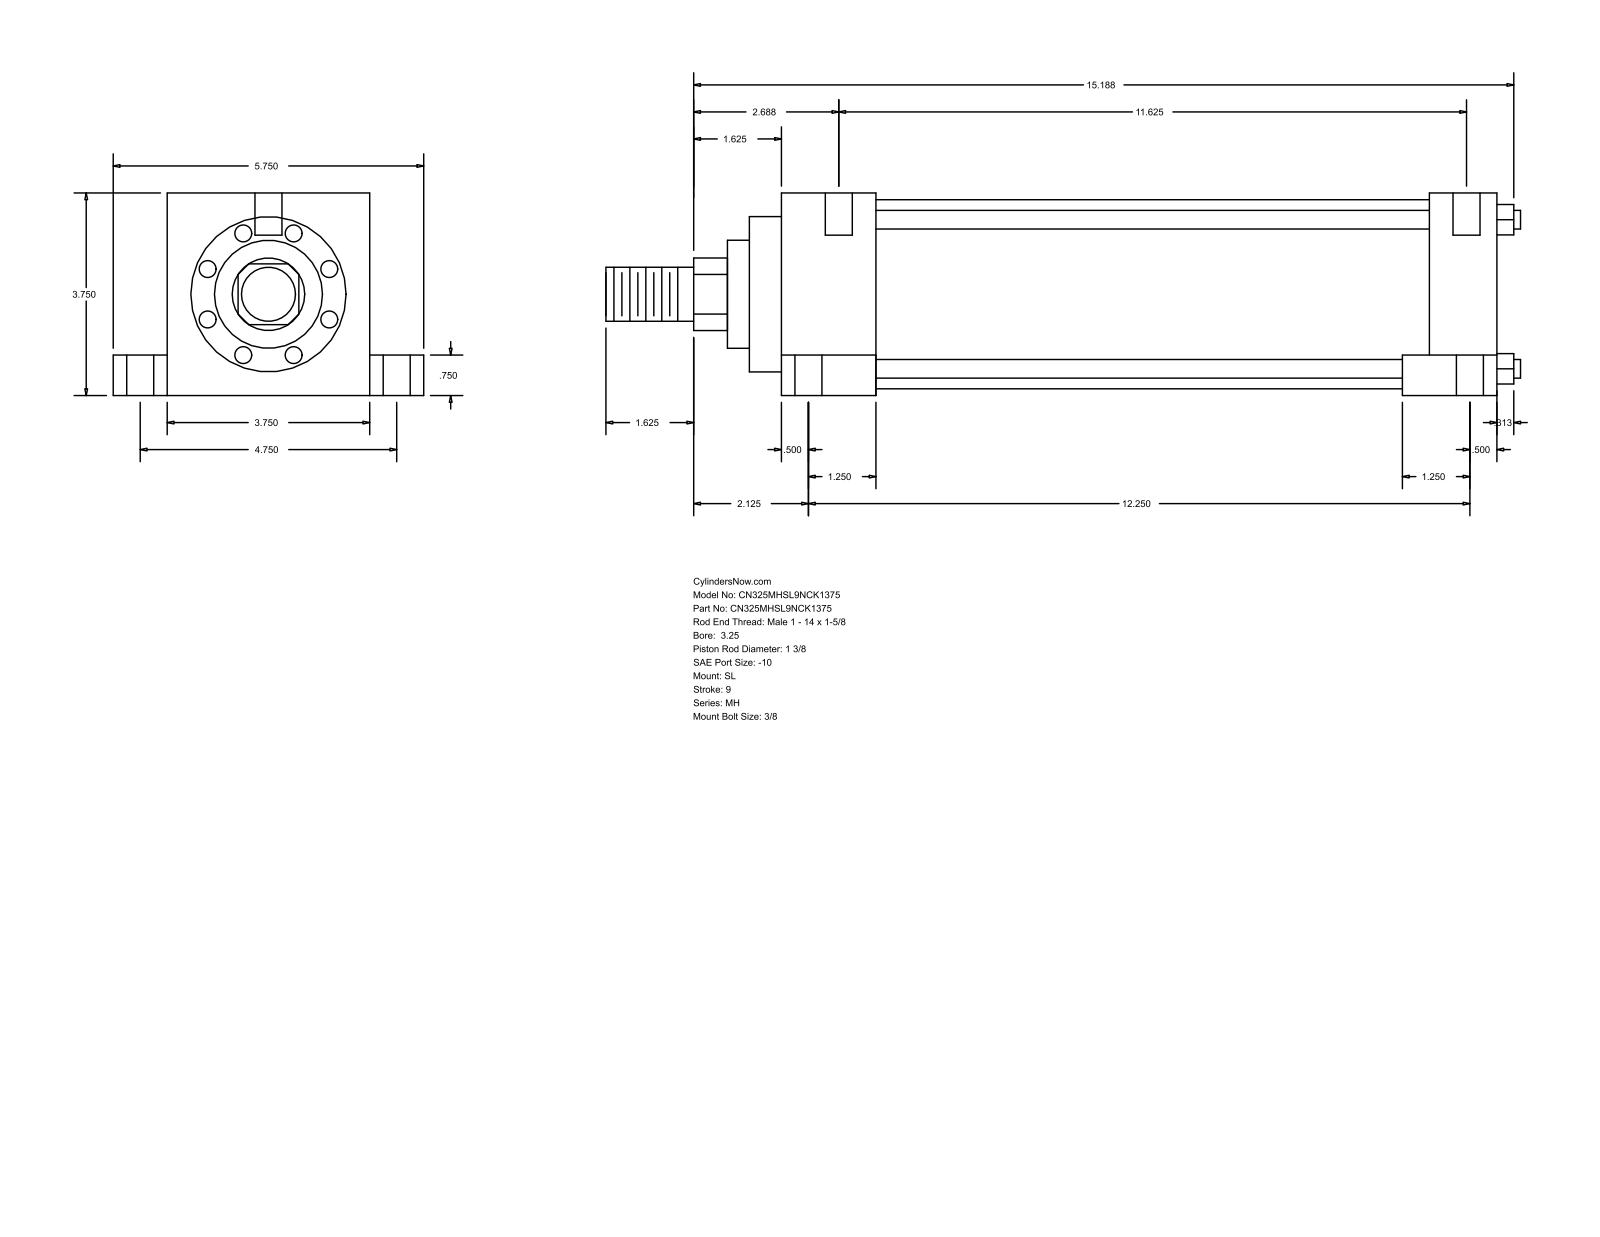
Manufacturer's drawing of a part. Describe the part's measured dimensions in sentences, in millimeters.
The part is named "MH_SL__0325_1.375". Its 3-D file was written by "GSSL Pune (CONFIG_CONTROL_DESIGN)". It is 0 solids with 110 faces: 77 planar, 33 cylindrical and 0 other. Overall it measures 430.21 by 146.05 by 95.25 millimeters. Round holes: 6 of diameter 12.7, 4 of diameter 5.56, 4 of diameter 19.05. Round bosses or shafts: 4 of diameter 8.76, 1 of diameter 88.9, 1 of diameter 73.03, 1 of diameter 50.8, 1 of diameter 34.92, 1 of diameter 25.4. Partial cylindrical surfaces (rounded edges, fillets, slot ends): 1 of radius 17.06. The main face-to-face distances are 95.24, 336.55, 44.45, 292.1, 25.41, 120.65, 19.05, 76.19, 304.8, 260.35. The hole center spacings are 60.35, 60.41, 61.65, 62, 120.66, 301.63, 302.93, 304.49.
